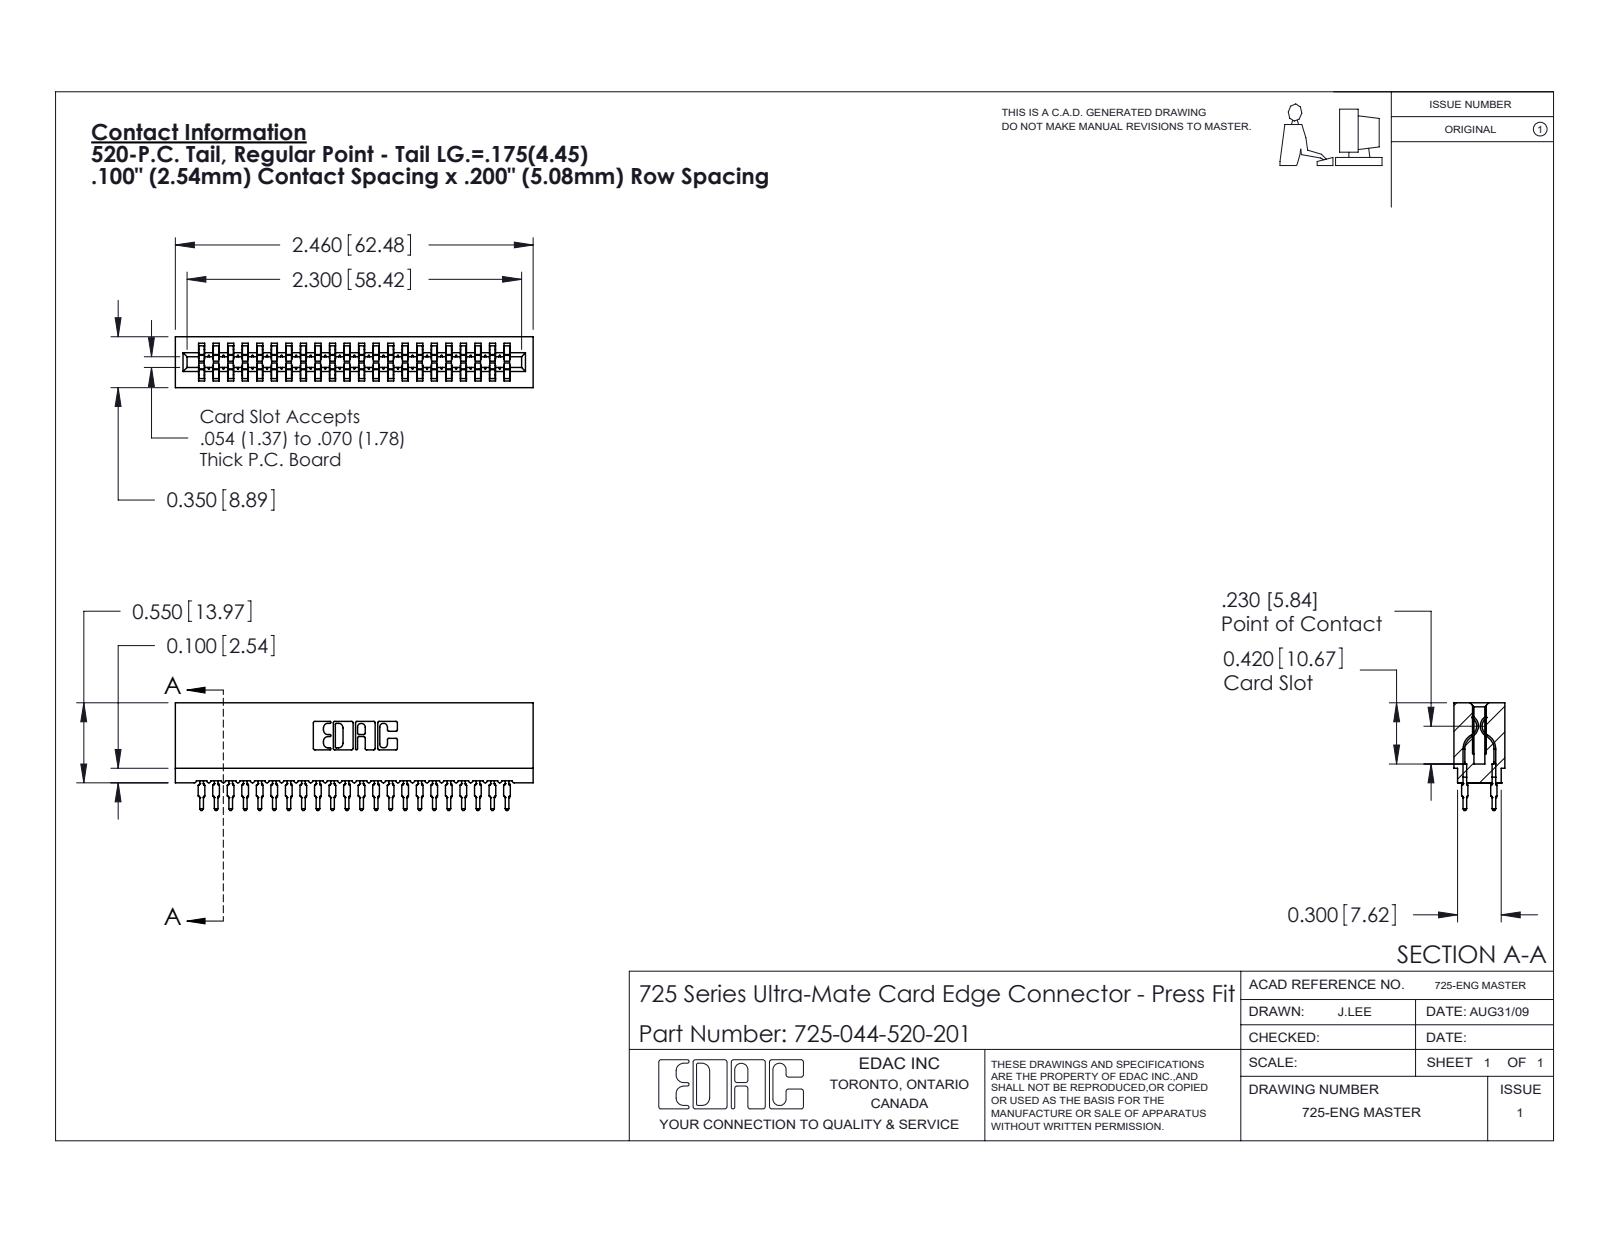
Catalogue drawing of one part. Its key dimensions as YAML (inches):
part_name: "725 Part_Insulator Option - 01; 745-292-001_520; 725-044-520-201"
step_written_by: "SolidWorks 2020 (CONFIG_CONTROL_DESIGN)"
units: inches
bodies: {solids: 45, faces: 4033, planar: 2079, cylindrical: 810, other: 1144}
overall_size: [2.46, 0.741, 0.35]
volume: 0.306
surface_area: 15.48
partial_cylinders:
  - {radius: 0.021, count: 88}
  - {radius: 0.015, count: 44}
  - {radius: 0.01, count: 22}
  - {radius: 0.005, count: 8}
  - {radius: 0.011, count: 8}
  - {radius: 0.007, count: 6}
  - {radius: 0.031, count: 6}
  - {radius: 0.026, count: 3}
face_to_face_distances: [0.2, 0.1, 0.4, 0.3, 0.5, 0.6, 0.35, 0.7, 0.063, 0.287]
